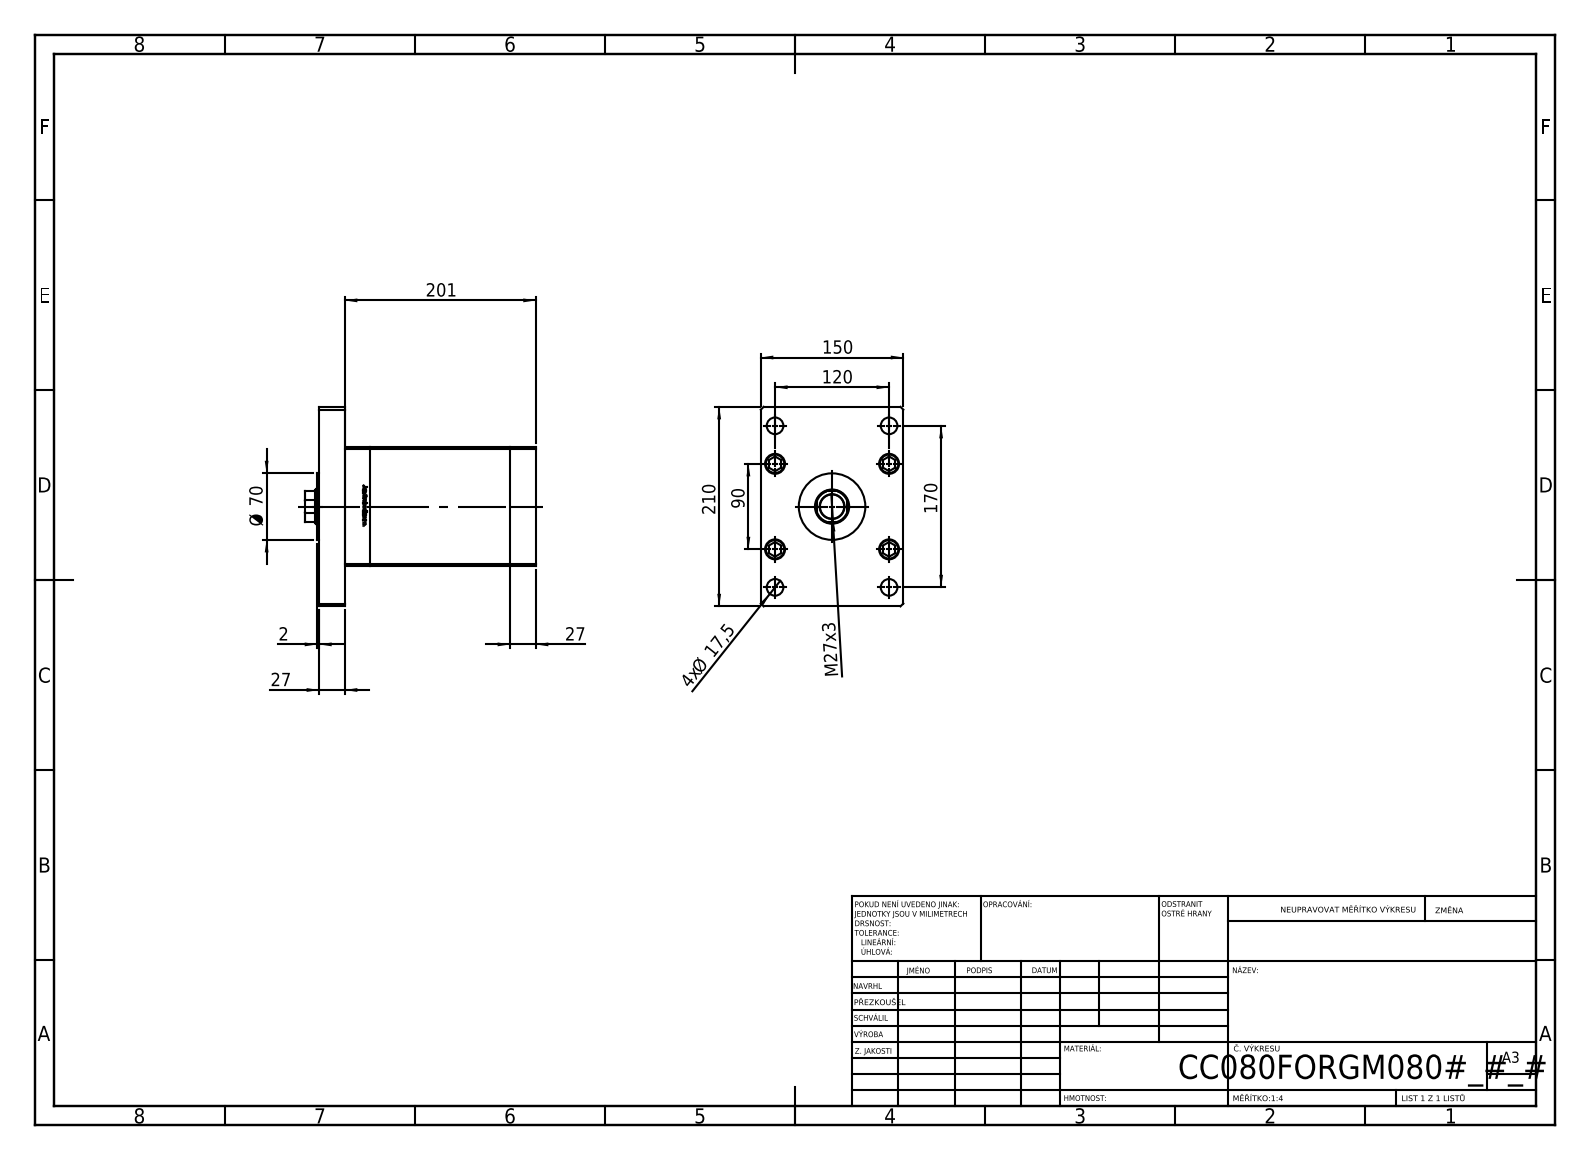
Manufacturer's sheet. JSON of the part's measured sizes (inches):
{"part_name": "ALLEN BOLT; V220C_F; V220C BACK_F; V220C_VC_F (+2 more)", "step_written_by": "SolidWorks 2019 (CONFIG_CONTROL_DESIGN)", "units": "inches", "bodies": {"solids": 19, "faces": 1298, "planar": 513, "cylindrical": 179, "other": 606}, "overall_size": [9.567, 8.268, 5.906], "volume_in3": 248.7, "surface_area_in2": 700.8, "round_holes": [[0.689, 9], [0.866, 5], [0.63, 4], [0.827, 4], [1.004, 1], [1.417, 1], [1.476, 1]], "round_bosses_or_shafts": [[0.315, 9], [0.827, 5], [3.15, 1], [2.756, 1]], "partial_cylinders_radius": [[0.037, 2], [0.689, 1]], "face_to_face_distances": [1.063, 6.85, 7.913, 5.906, 5.787, 2.126, 4.921, 6.594, 8.976, 1.319], "hole_center_spacings": [2.008, 1.575, 2.953, 4.096, 4.724, 4.98, 5.118, 6.965]}
